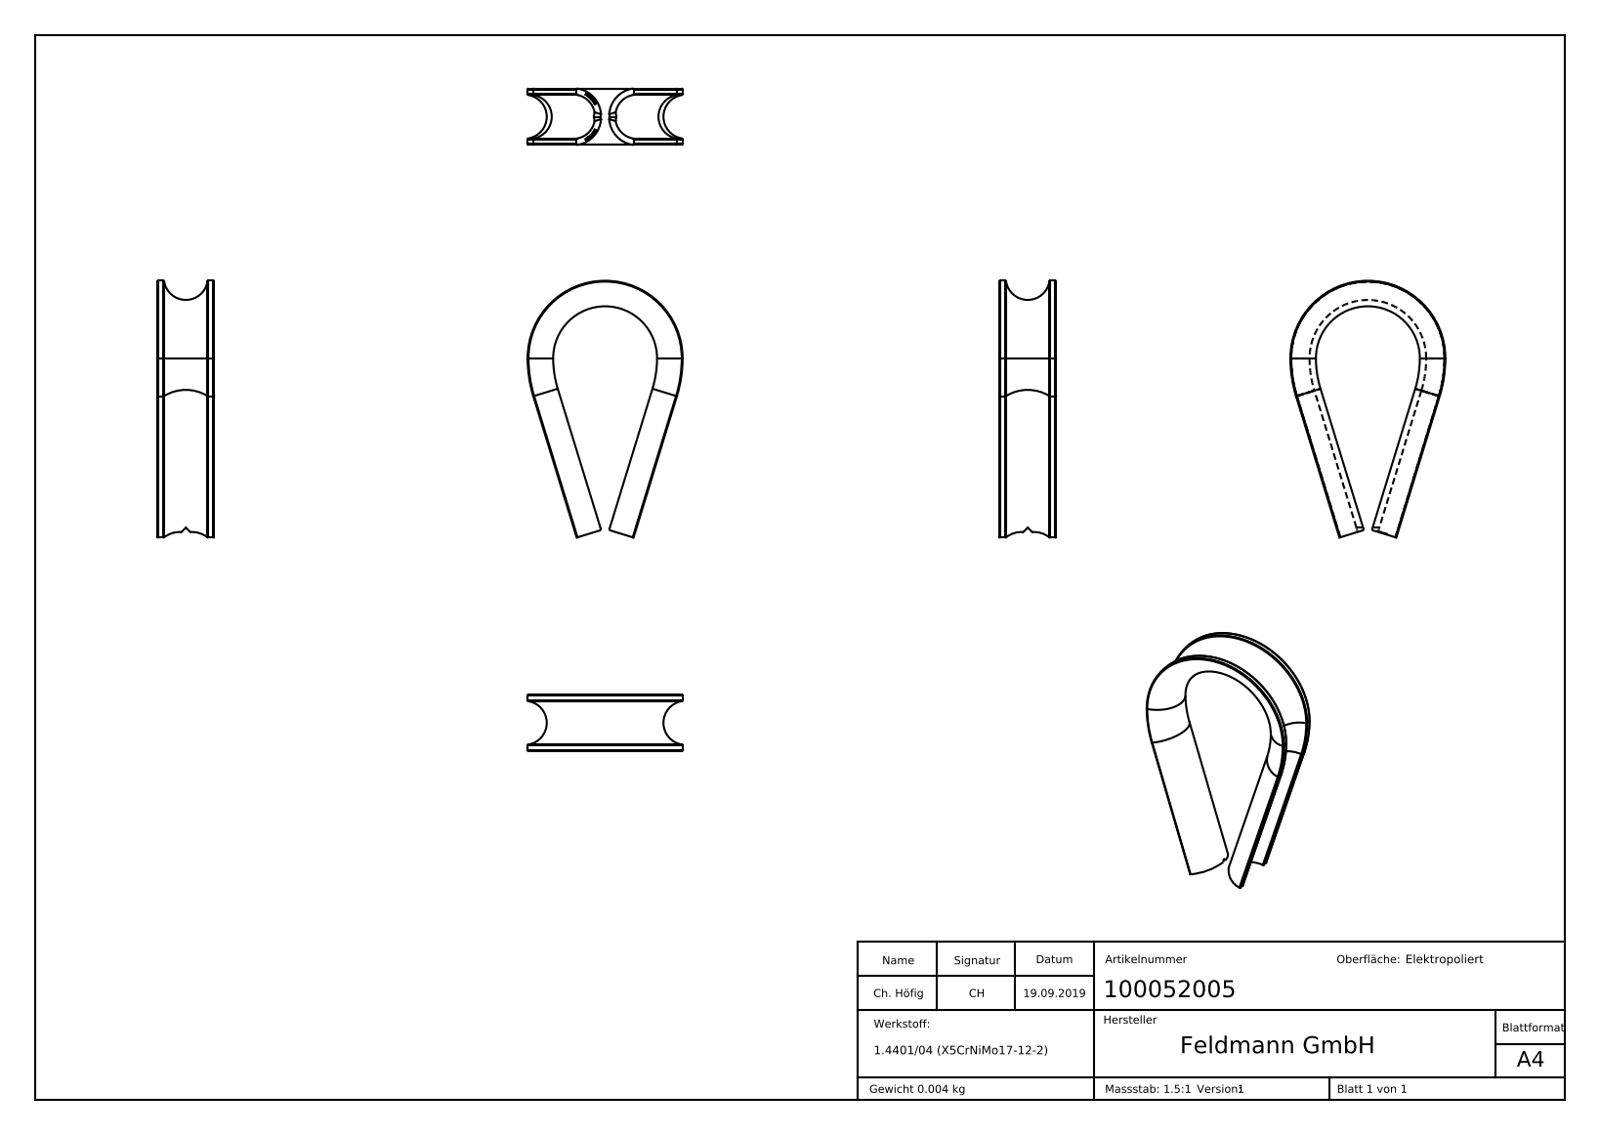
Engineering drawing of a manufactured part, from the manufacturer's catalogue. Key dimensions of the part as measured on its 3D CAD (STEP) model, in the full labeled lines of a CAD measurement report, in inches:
Part name (STEP PRODUCT): 100052005
STEP written by: SolidWorks 2015 (CONFIG_CONTROL_DESIGN)
Units: inches
Bodies: 1 solid, 274 faces (115 planar, 20 cylindrical, 139 other)
Overall size (bounding box): 1.265 × 0.764 × 0.277
Volume: 0.032 in³ · Surface area: 2.201 in²
Partial cylindrical surfaces — rounded edges, fillets, slot ends (radius × count): R0.004 ×8, R0.108 ×2, R0.14 ×2, R0.638 ×2, R0.382 ×1
